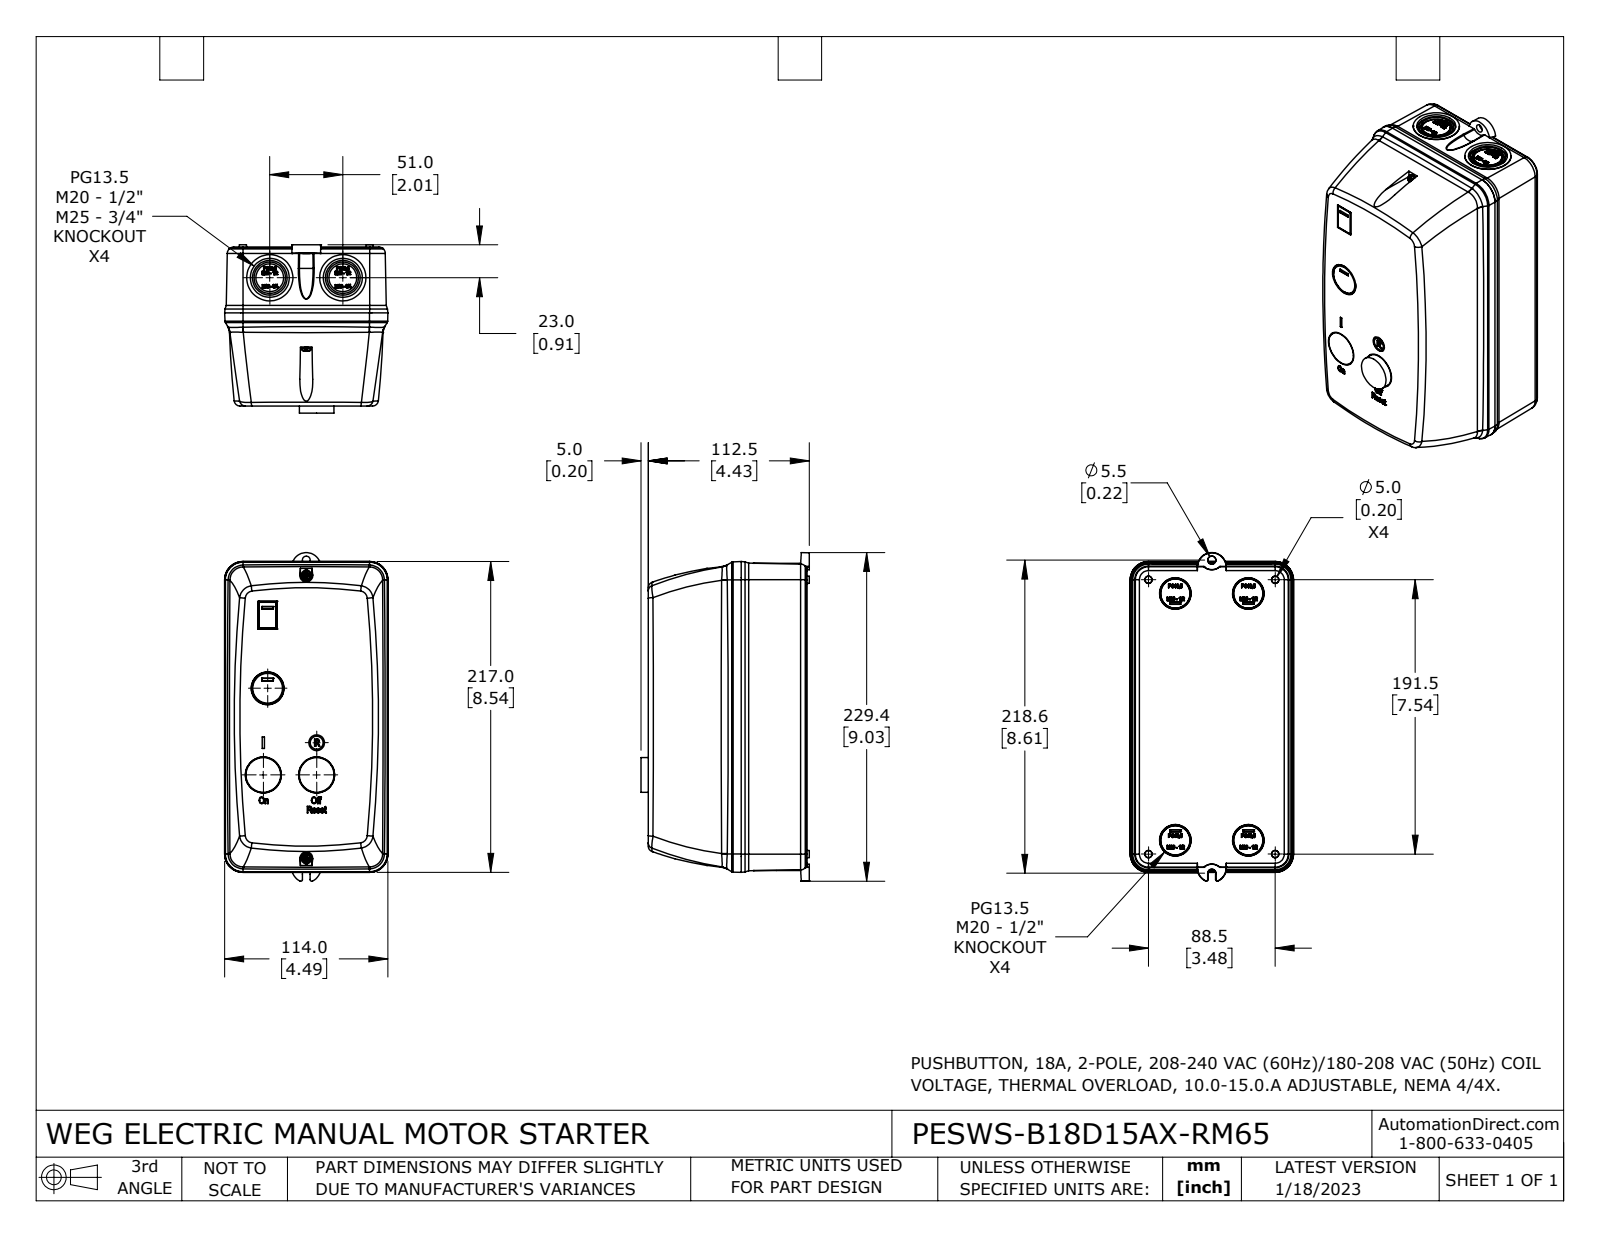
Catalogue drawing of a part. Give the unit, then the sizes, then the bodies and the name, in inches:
Units: inches
Overall size (bounding box): 9.033 × 4.626 × 4.489
Round holes (diameter × count): ⌀0.173 ×2, ⌀0.863 ×2, ⌀1.072 ×2, ⌀0.217 ×1, ⌀0.433 ×1
Round bosses / shafts (diameter × count): ⌀1.27 ×2, ⌀0.955 ×2, ⌀0.953 ×2, ⌀0.763 ×2, ⌀0.276 ×2, ⌀0.118 ×2, ⌀0.354 ×1
Partial cylindrical surfaces — rounded edges, fillets, slot ends (radius × count): R0.079 ×4, R0.181 ×4, R0.376 ×4, R0.257 ×2, R0.297 ×2, R0.082 ×1, R0.085 ×1, R0.108 ×1
Main face-to-face distances: 1.811, 2.559, 4.37, 0.02, 4.35, 1.791, 4.331, 0.039, 4.311, 2.52
Hole centre spacings: 0.413, 2.008, 3.202, 4.615, 5.028, 7.795, 8.209
Volume: 149.9 in³ · Surface area: 257.6 in²
Bodies: 6 solids, 2195 faces (1110 planar, 92 cylindrical, 993 other)
Part name (STEP PRODUCT): PESWS-B18D15AX-RM65
STEP written by: SolidWorks 2021 (CONFIG_CONTROL_DESIGN)
